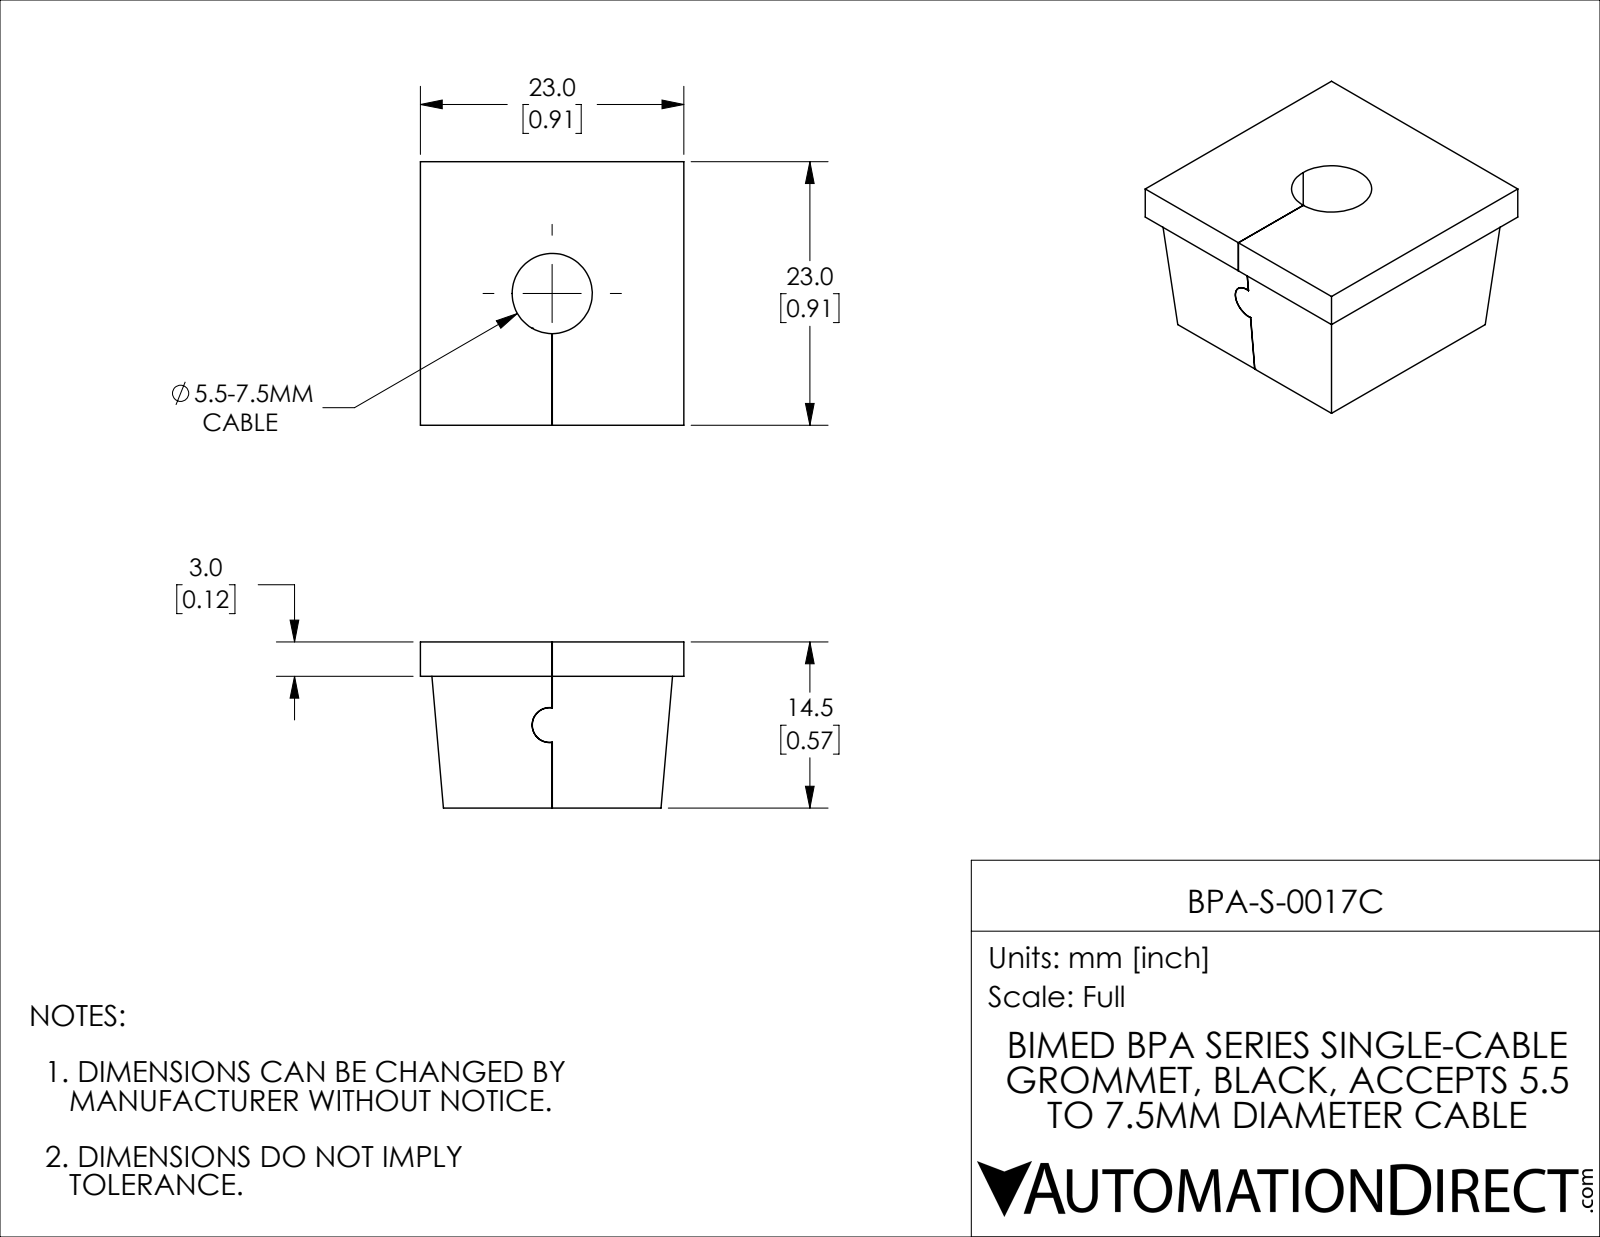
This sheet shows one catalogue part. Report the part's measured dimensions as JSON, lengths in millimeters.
{"part_name": "BPA-S-0017C", "step_written_by": "SolidWorks 2021 (CONFIG_CONTROL_DESIGN)", "units": "millimeters", "bodies": {"solids": 1, "faces": 24, "planar": 17, "cylindrical": 7, "other": 0}, "overall_size": [23, 23, 14.5], "volume_mm3": 5629, "surface_area_mm2": 2647, "round_holes": [[7, 1]], "partial_cylinders_radius": [[1.52, 1], [1.53, 1]], "face_to_face_distances": [14.5, 11.5, 23, 3, 11.51, 11.49]}
